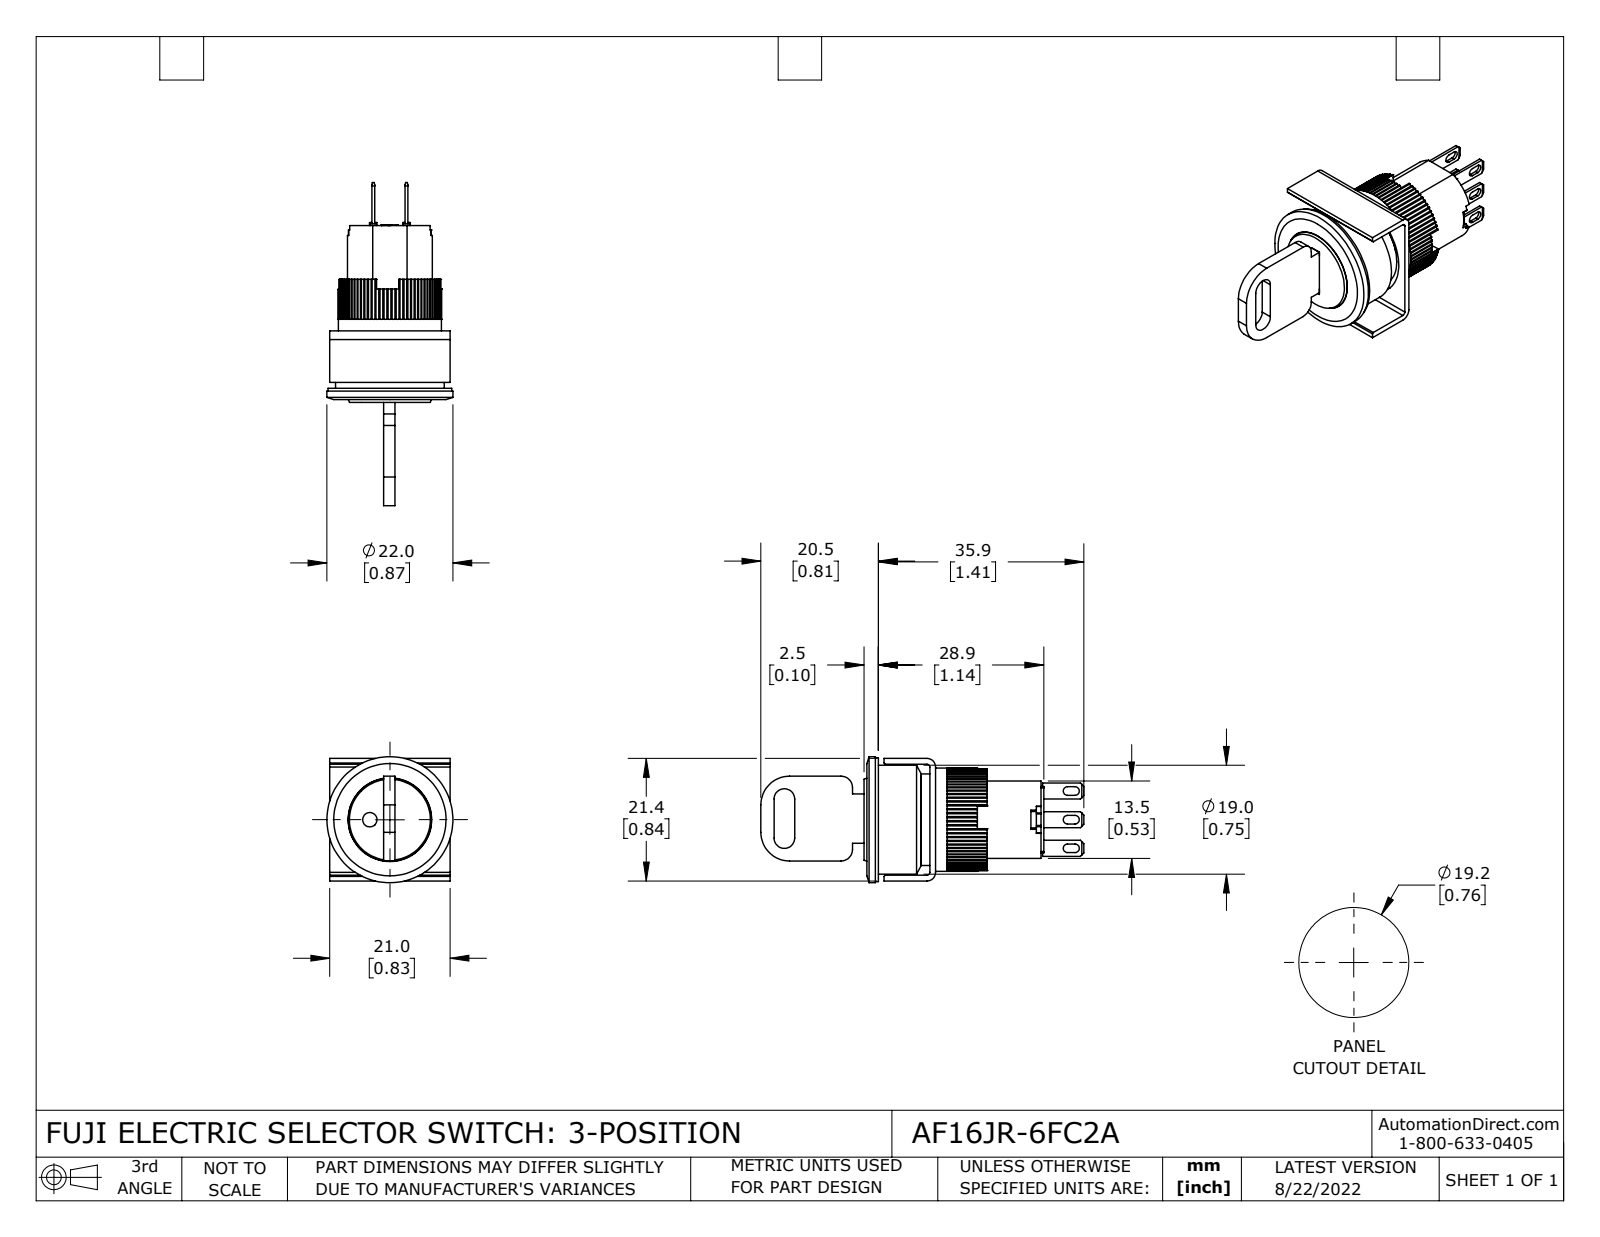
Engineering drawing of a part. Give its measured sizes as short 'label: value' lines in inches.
name: AF16JR-6FC2A
written by: SolidWorks 2021 (CONFIG_CONTROL_DESIGN)
unit: in
bodies: 13 solids, 707 faces (518 planar, 183 cylindrical, 6 other)
size: 2.22 × 0.866 × 0.866
volume: 0.495 in³; area: 11.24 in²
holes: 1× ⌀0.039, 1× ⌀0.098, 1× ⌀0.575, 1× ⌀0.709, 1× ⌀0.748
bosses: 1× ⌀0.866, 1× ⌀0.85, 1× ⌀0.63, 1× ⌀0.583, 1× ⌀0.571
rounds: 80× R0.01, 12× R0.008, 6× R0.03, 2× R0.02, 2× R0.059, 2× R0.071, 2× R0.079, 2× R0.197
face distances: 0.079, 0.039, 0.02, 0.374, 0.177, 0.098, 0.394, 0.803, 0.059, 0.764
hole spacings: 0.138
